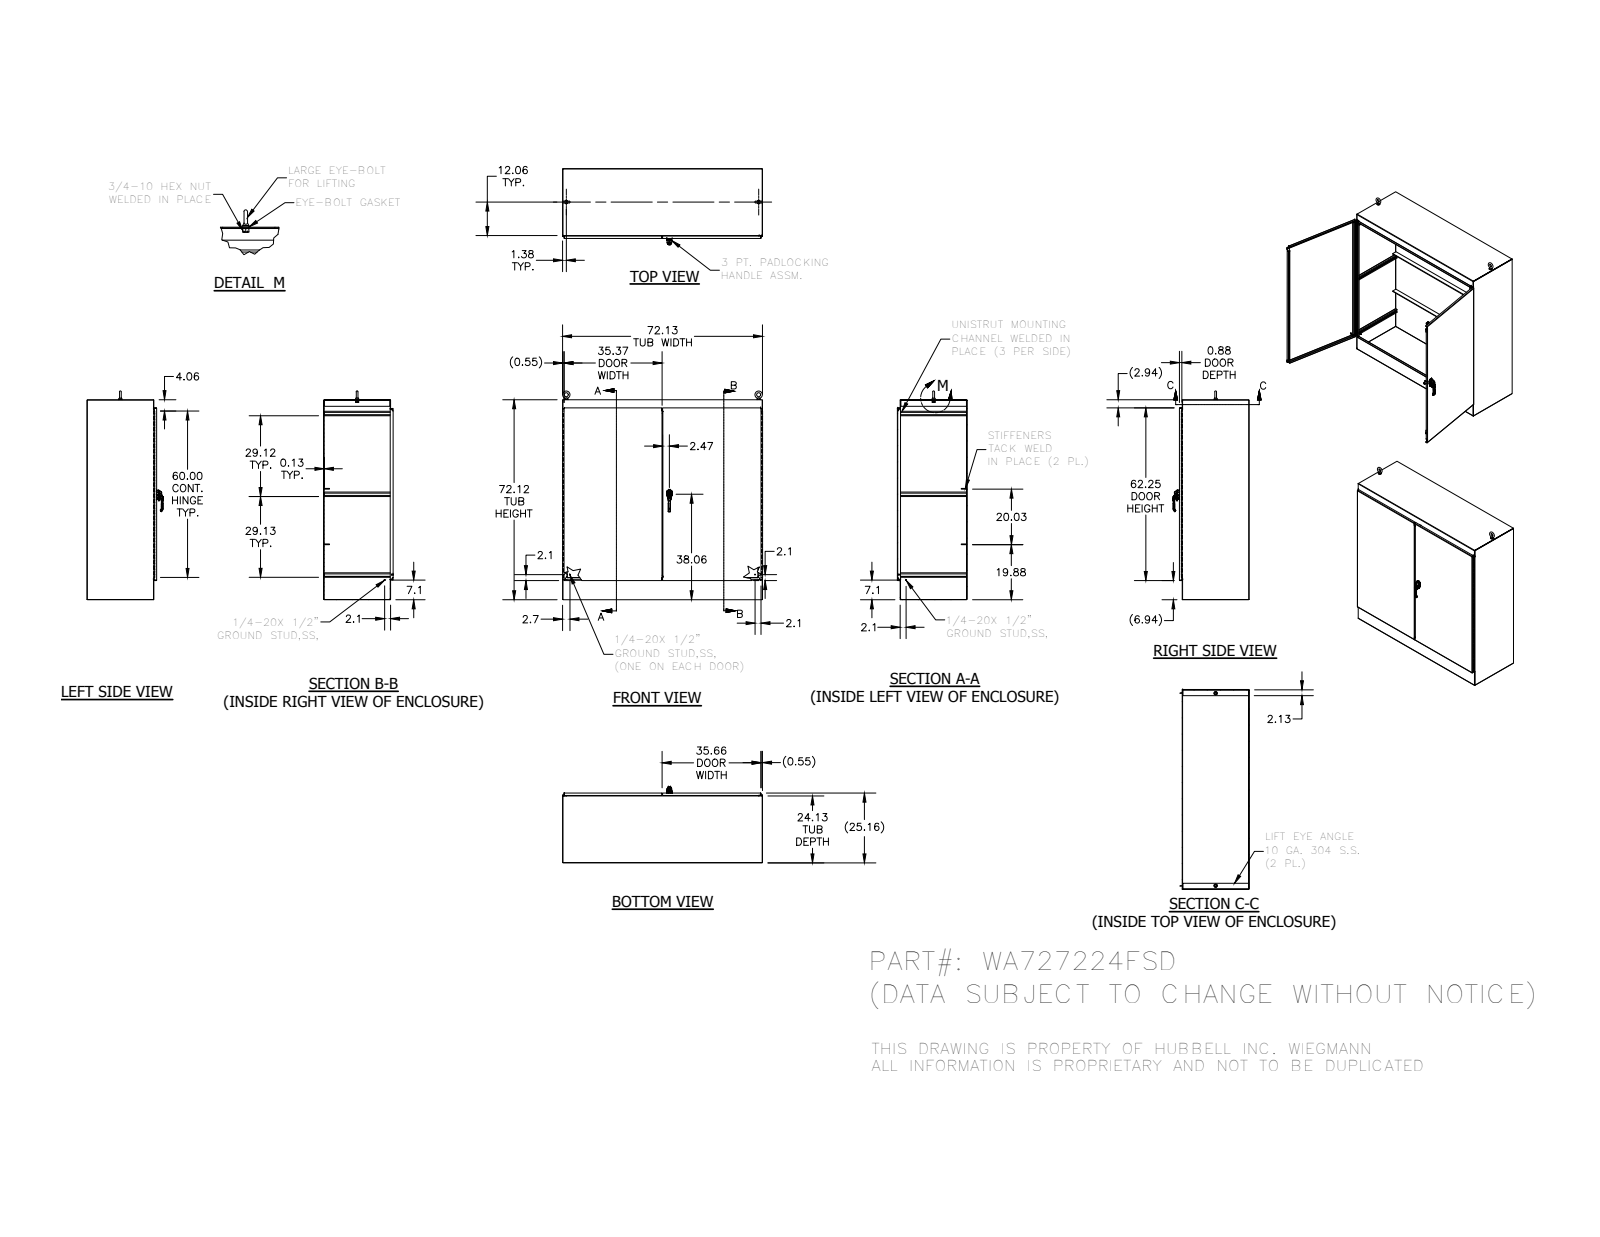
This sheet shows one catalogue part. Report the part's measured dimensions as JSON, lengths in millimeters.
{"part_name": "FUN00103; HFW3025; 316298; 349132 (+8 more)", "step_written_by": "Autodesk Inventor 2014 (AUTOMOTIVE_DESIGN)", "units": "millimeters", "bodies": {"solids": 66, "faces": 3780, "planar": 1777, "cylindrical": 1263, "other": 740}, "overall_size": [1911.29, 1832.34, 696.76], "volume_mm3": 41090000, "surface_area_mm2": 25840000, "round_holes": [[7.02, 8], [5.08, 4], [5.4, 3], [6, 3], [7.11, 3], [3.17, 2], [6.13, 2], [6.35, 2], [6.41, 2], [10.16, 2], [10.33, 2], [10.5, 2]], "round_bosses_or_shafts": [[6.35, 5], [8.56, 3], [31.75, 2], [28.45, 2], [25.4, 2], [19.05, 2], [14.29, 2], [13.37, 2]], "partial_cylinders_radius": [[0.5, 164], [0.3, 84], [0.79, 24], [3.97, 21], [0.47, 19], [0.25, 16], [2, 15], [1.27, 14]], "face_to_face_distances": [3.18, 1828.8, 3.17, 635.97, 632.79, 639.14, 635.96, 1825.62, 1831.98, 609.6], "hole_center_spacings": [6, 6.5, 9.67, 9.69, 9.72, 12.49, 12.5, 19.36]}
